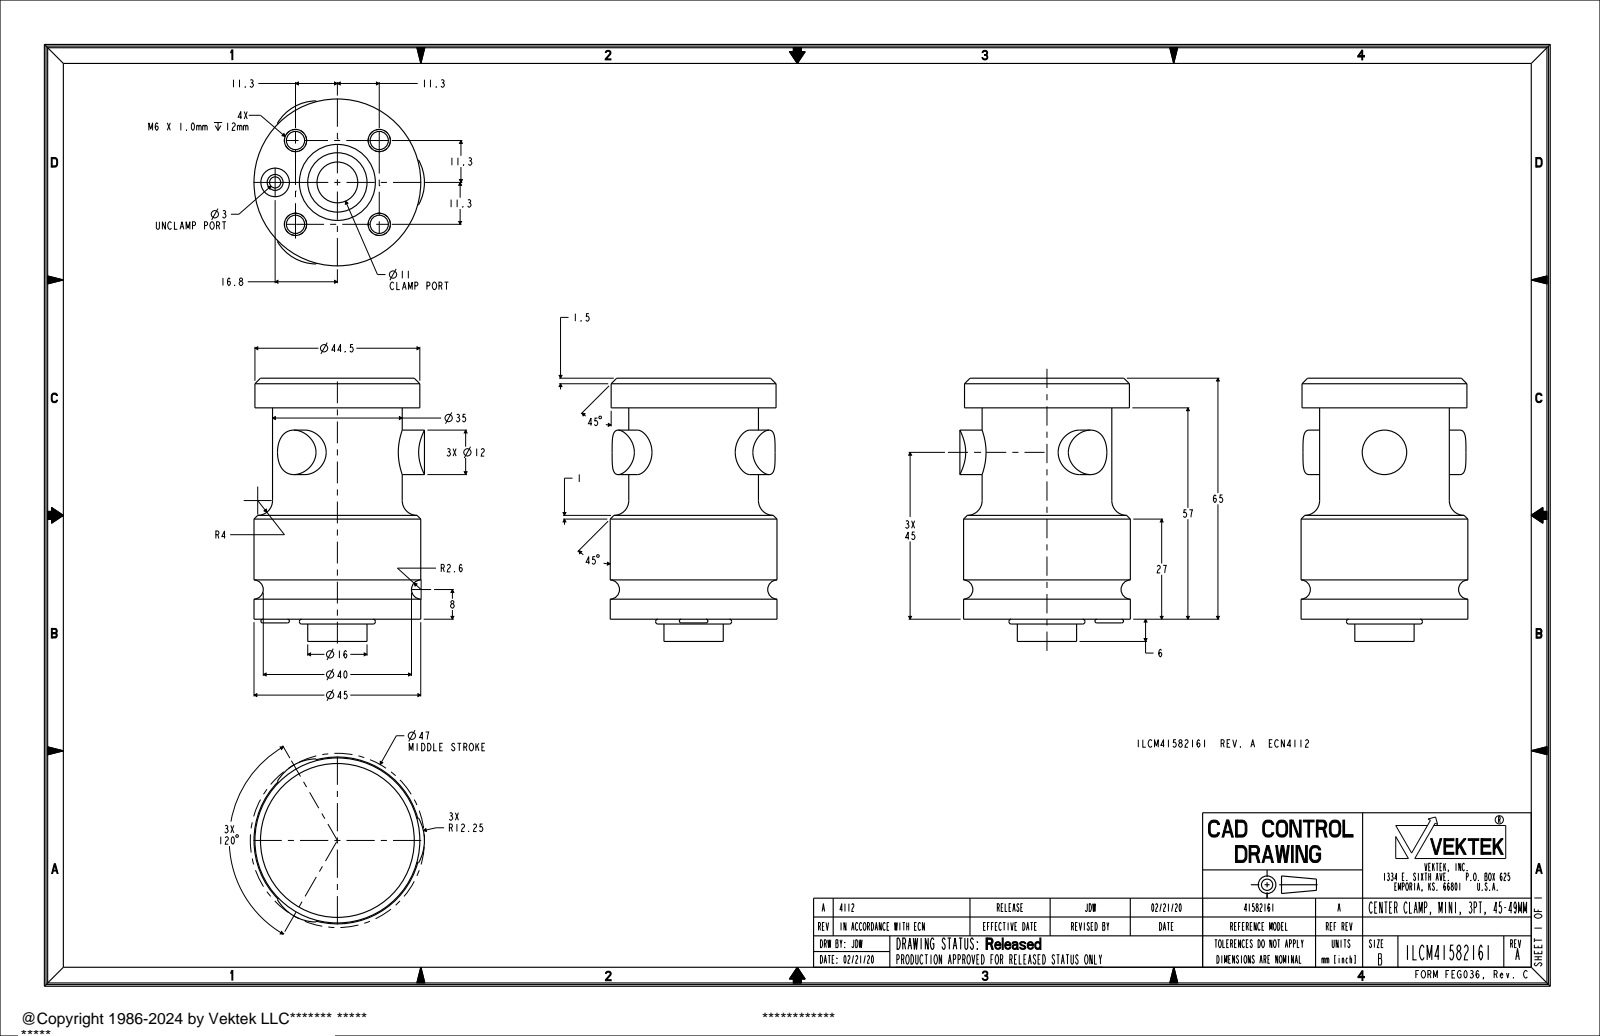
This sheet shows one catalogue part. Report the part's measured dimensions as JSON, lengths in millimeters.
{"part_name": "ILCM41582161", "step_written_by": "PRO/ENGINEER BY PARAMETRIC TECHNOLOGY CORPORATION, 2013320 (AUTOMOTIVE_DESIGN)", "units": "millimeters", "bodies": {"solids": 1, "faces": 97, "planar": 18, "cylindrical": 43, "other": 36}, "overall_size": [71, 46, 45], "volume_mm3": 85476, "surface_area_mm2": 15891, "round_holes": [[4.92, 4], [3, 1], [11, 1]], "round_bosses_or_shafts": [[6, 4], [12, 3], [45, 1], [44.5, 1], [35, 1], [20.5, 1], [16, 1]], "partial_cylinders_radius": [[12.25, 3]], "face_to_face_distances": [65, 8, 57, 63, 1, 58, 66, 5, 6, 71], "hole_center_spacings": [15.98, 22.6, 12.57, 30.29, 31.96, 16.8]}
